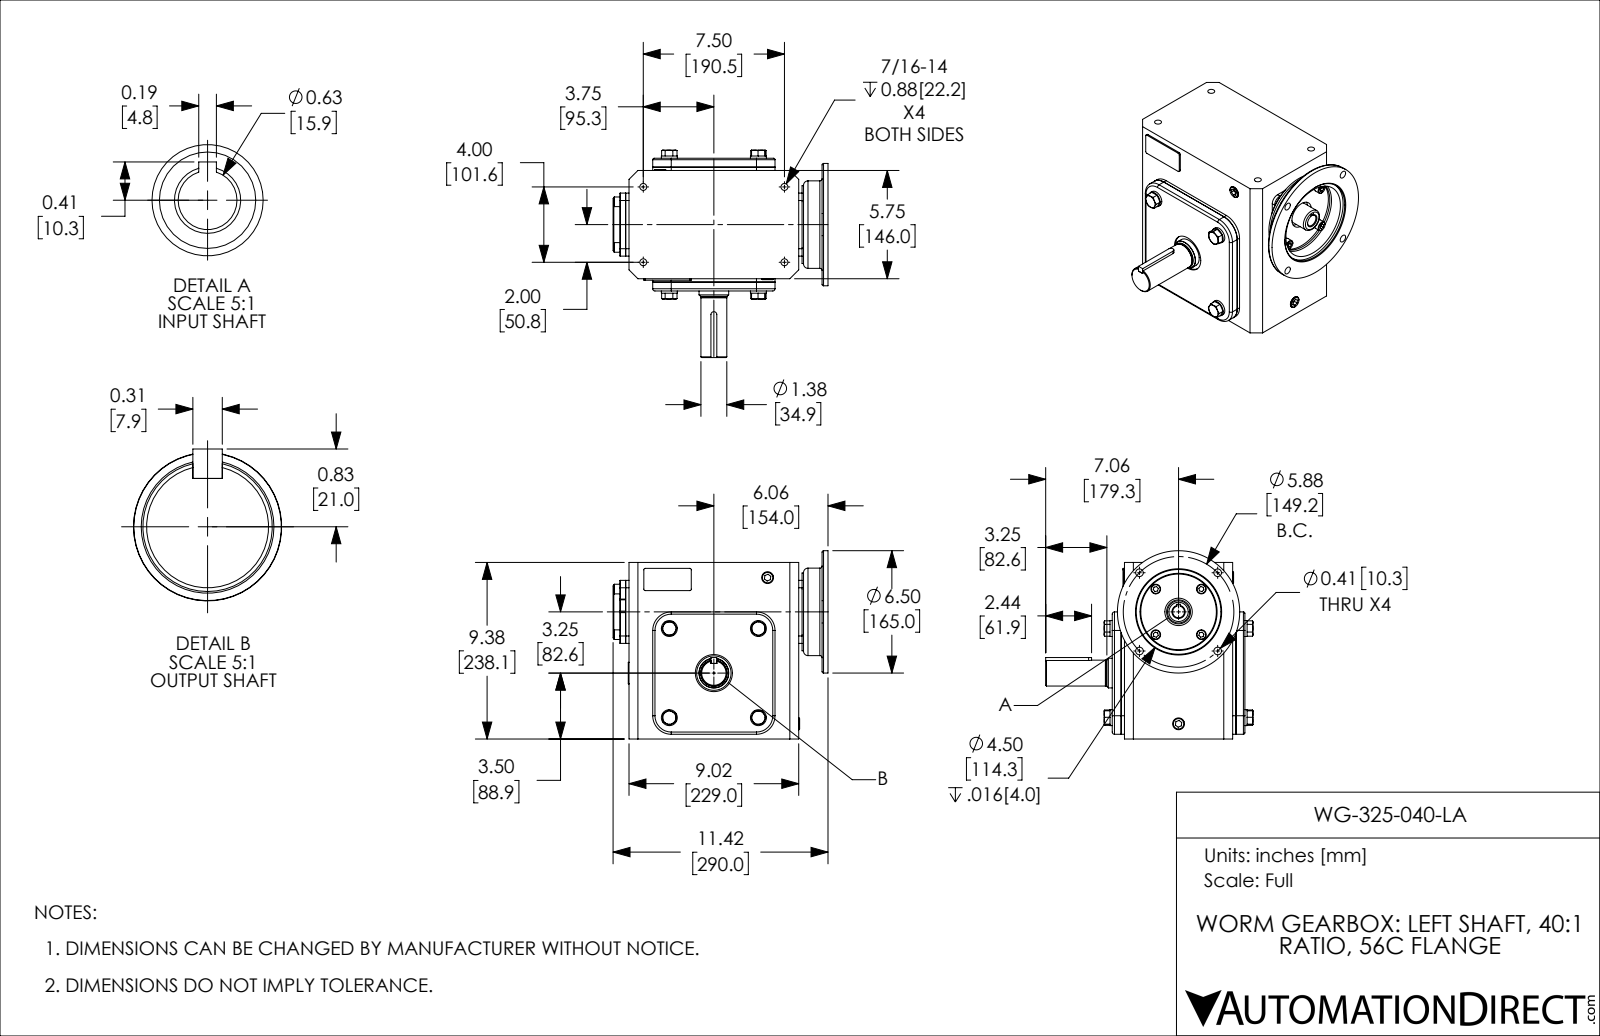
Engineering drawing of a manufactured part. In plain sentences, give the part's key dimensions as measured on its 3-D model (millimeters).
The part is named "WG-325-040-LA". Its 3-D file was written by "SolidWorks 2017 (AUTOMOTIVE_DESIGN)". It is 39 solids with 575 faces: 318 planar, 167 cylindrical and 90 other. Overall it measures 290 by 279.8 by 253.9 millimeters. Its volume is 8 251 000 cubic millimeters and its surface area 578 800 square millimeters. Round holes: 4 of diameter 9.3, 4 of diameter 10.3, 3 of diameter 16, 1 of diameter 15, 1 of diameter 15.9, 1 of diameter 24.8, 1 of diameter 30, 1 of diameter 37, 1 of diameter 50, 1 of diameter 62, 1 of diameter 70, 1 of diameter 102. Round bosses or shafts: 4 of diameter 21.5, 4 of diameter 13, 1 of diameter 165, 1 of diameter 118, 1 of diameter 105, 1 of diameter 72, 1 of diameter 40, 1 of diameter 34.9. Partial cylindrical surfaces (rounded edges, fillets, slot ends): 11 of radius 2, 4 of radius 3, 4 of radius 10, 4 of radius 23, 4 of radius 25, 2 of radius 0.5, 2 of radius 1, 1 of radius 4. The main face-to-face distances are 2, 4.5, 165, 10, 177, 12, 167, 162.5, 14.5, 16.5. The hole center spacings are 74.6, 105.5, 60.6, 101.6, 111.5, 145.2, 147.8, 149.2.
